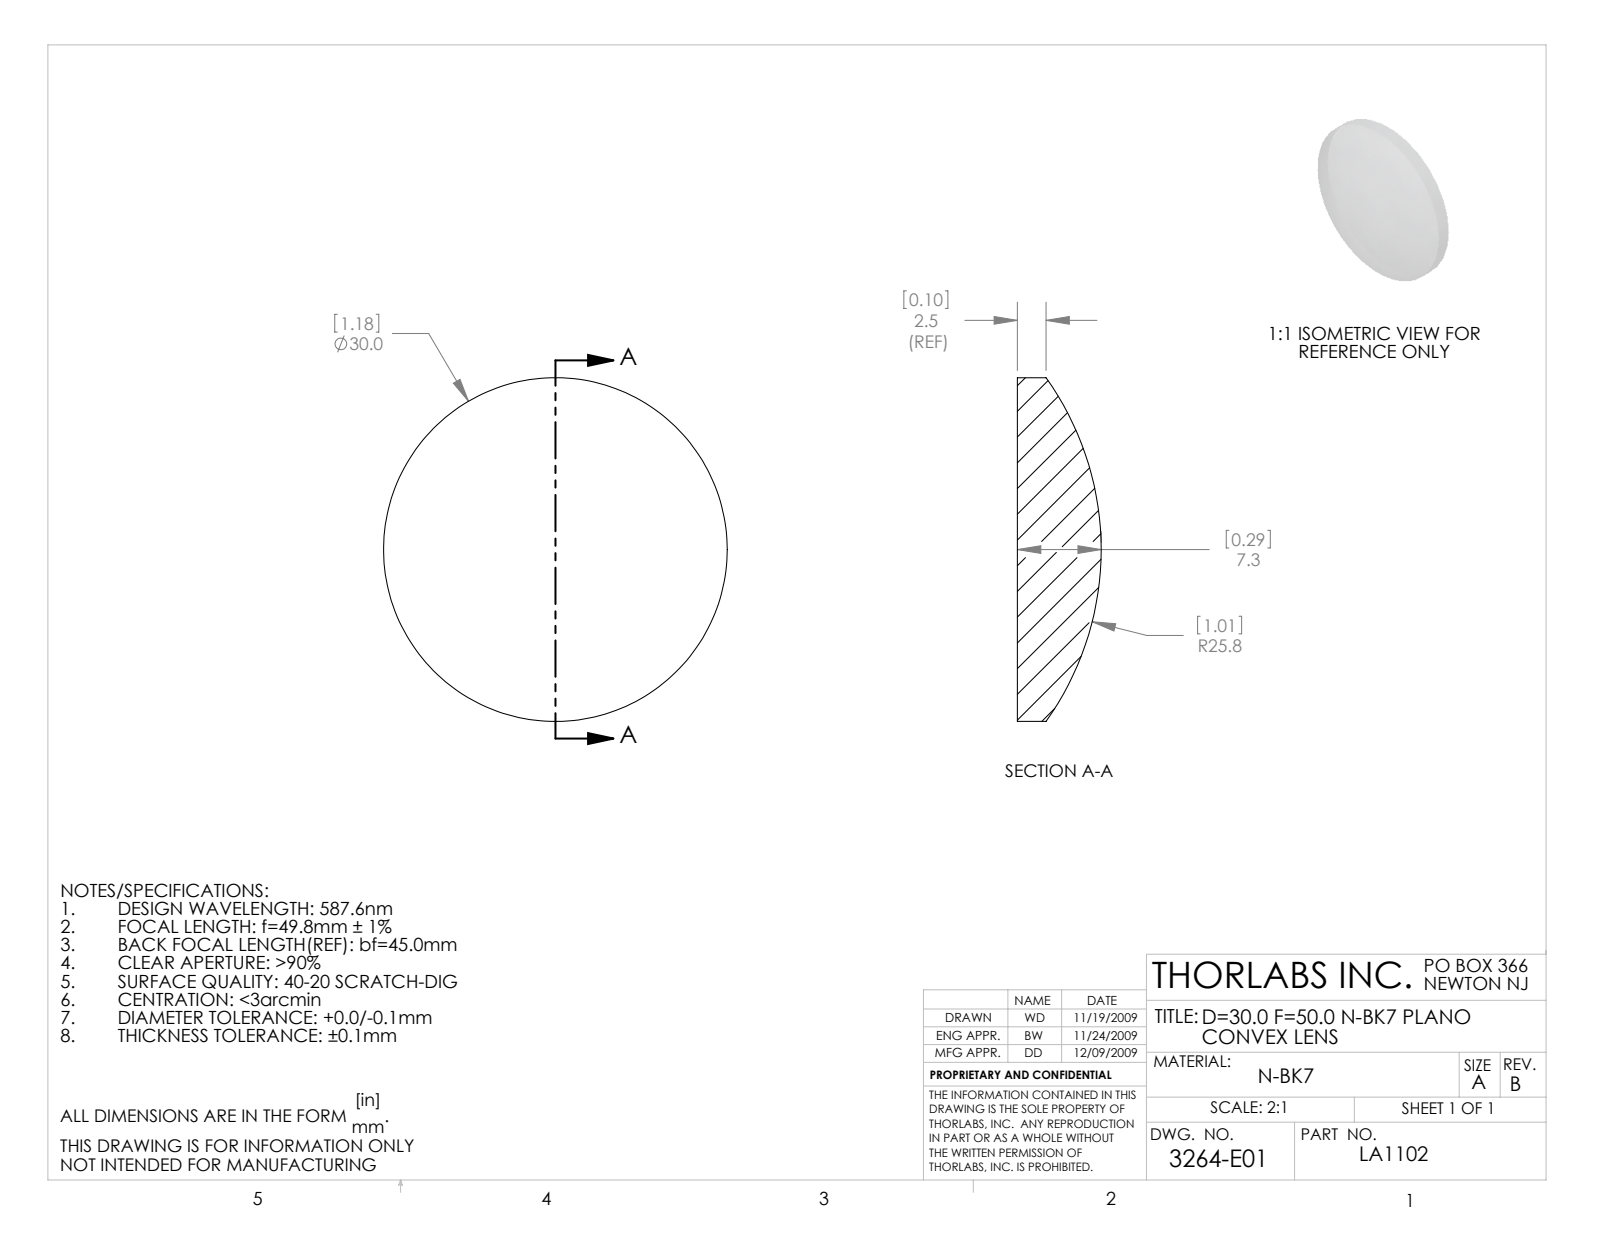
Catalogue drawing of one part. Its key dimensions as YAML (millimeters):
part_name: "3264-E0W"
step_written_by: "SolidWorks 2009 (AUTOMOTIVE_DESIGN)"
units: millimeters
bodies: {solids: 1, faces: 5, planar: 1, cylindrical: 2, other: 2}
overall_size: [30, 30, 7.31]
volume: 3522
surface_area: 1721
round_bosses_or_shafts:
  - {diameter: 30, count: 1}
